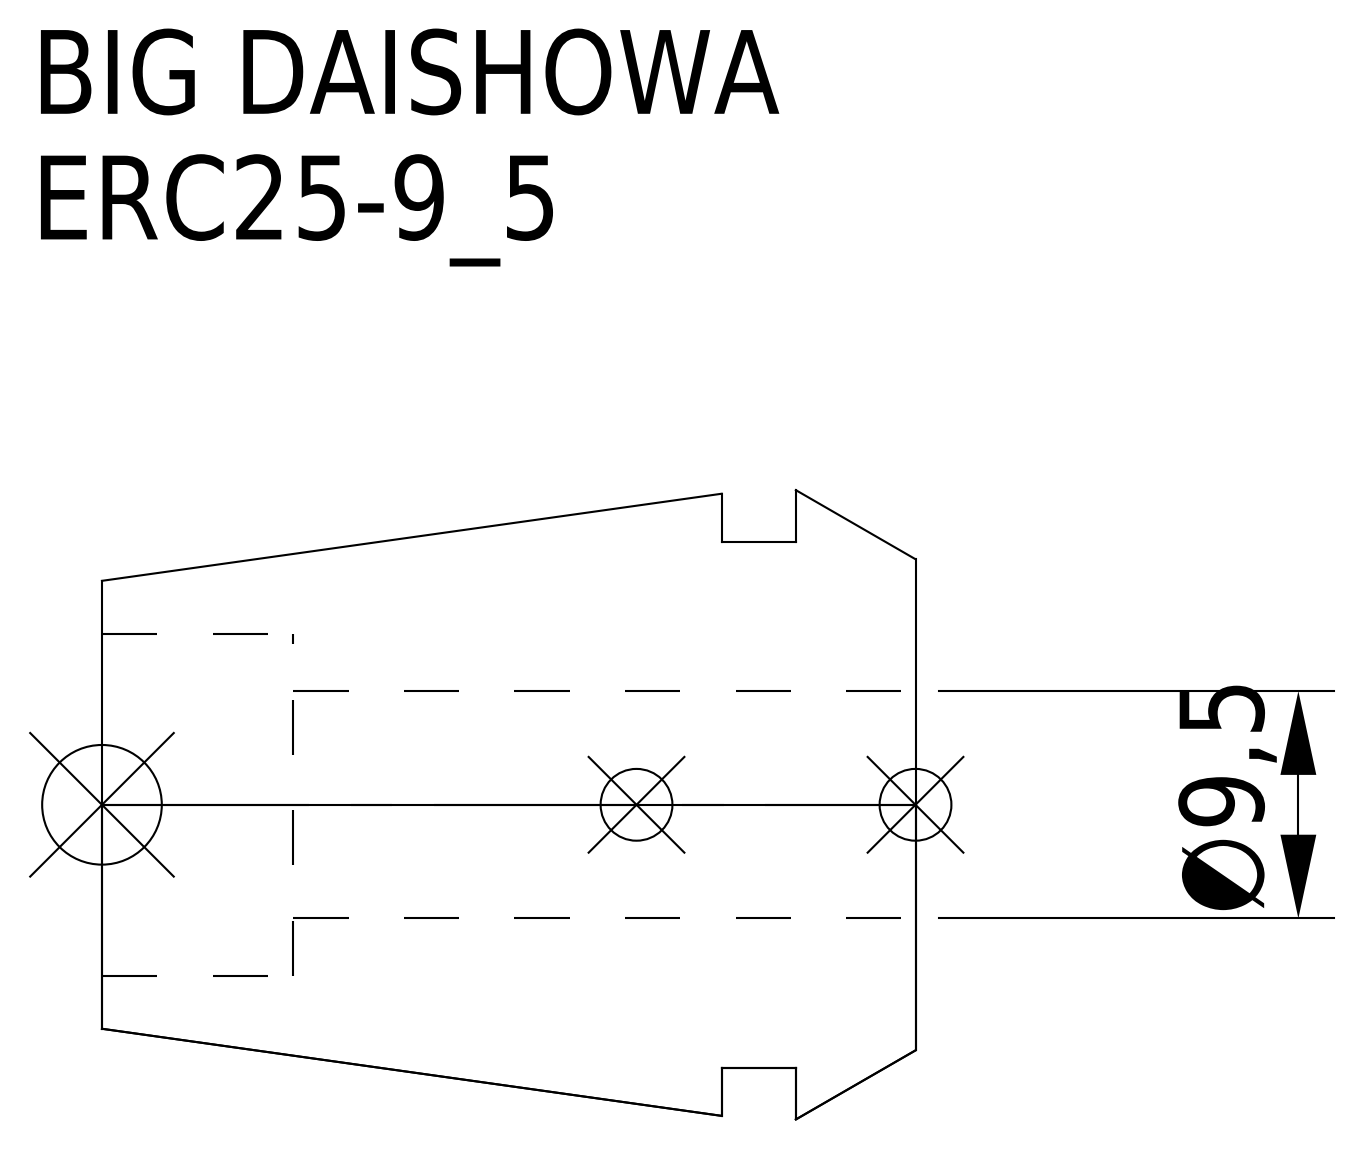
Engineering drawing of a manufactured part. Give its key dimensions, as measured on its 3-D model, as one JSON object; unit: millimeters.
{"part_name": "ERC25-9_5", "step_written_by": "CREO PARAMETRIC BY PTC INC, 2016380 (AUTOMOTIVE_DESIGN)", "units": "millimeters", "bodies": {"solids": 1, "faces": 15, "planar": 5, "cylindrical": 6, "other": 4}, "overall_size": [34, 26.3, 26.3], "volume_mm3": 10475, "surface_area_mm2": 4390, "round_holes": [[9.5, 1], [14.3, 1]], "round_bosses_or_shafts": [[22, 1]], "face_to_face_distances": [5, 8.1, 3.1, 34, 29, 25.9, 26, 21, 17.9, 8]}
